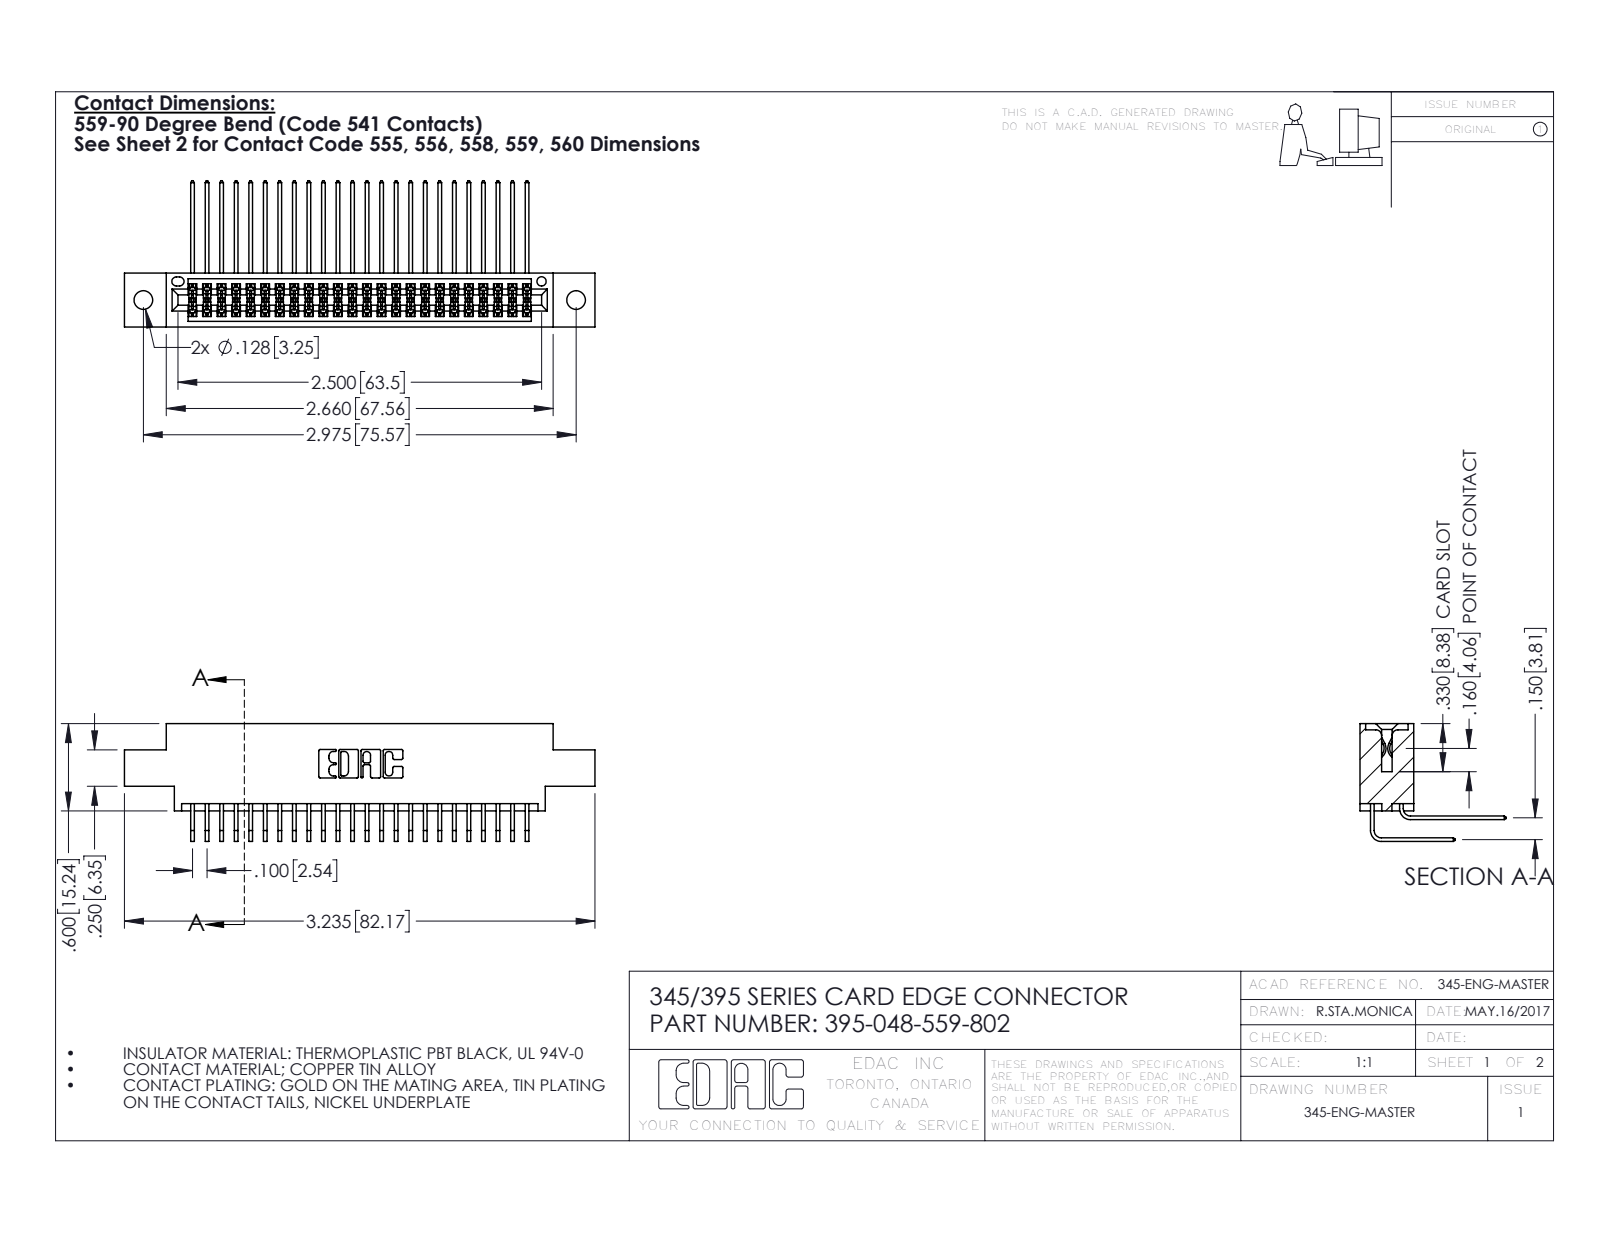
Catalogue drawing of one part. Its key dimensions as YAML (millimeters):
part_name: "395-048-559-802; 345-292-001_559 Tail - 2; 345 Part_0.170 Offset - 0.128 Dia; 345-292-001_558 559 Tail - 1"
step_written_by: "SolidWorks 2016 (CONFIG_CONTROL_DESIGN)"
units: millimeters
bodies: {solids: 49, faces: 2626, planar: 1764, cylindrical: 862, other: 0}
overall_size: [82.2, 25.5, 20.5]
volume: 7950
surface_area: 12560
round_holes:
  - {diameter: 3.3, count: 2}
  - {diameter: 1.6, count: 1}
partial_cylinders:
  - {radius: 0.2, count: 72}
  - {radius: 0.3, count: 22}
  - {radius: 0.2, count: 6}
  - {radius: 0.8, count: 6}
  - {radius: 0.7, count: 3}
  - {radius: 0.4, count: 2}
  - {radius: 0.5, count: 2}
  - {radius: 0.6, count: 2}
face_to_face_distances: [1.8, 7.6, 9.4, 5.1, 2.5, 6.9, 0.6, 3.8, 5.7, 4.4]
hole_center_spacings: [6.9, 69.6, 75.6]
